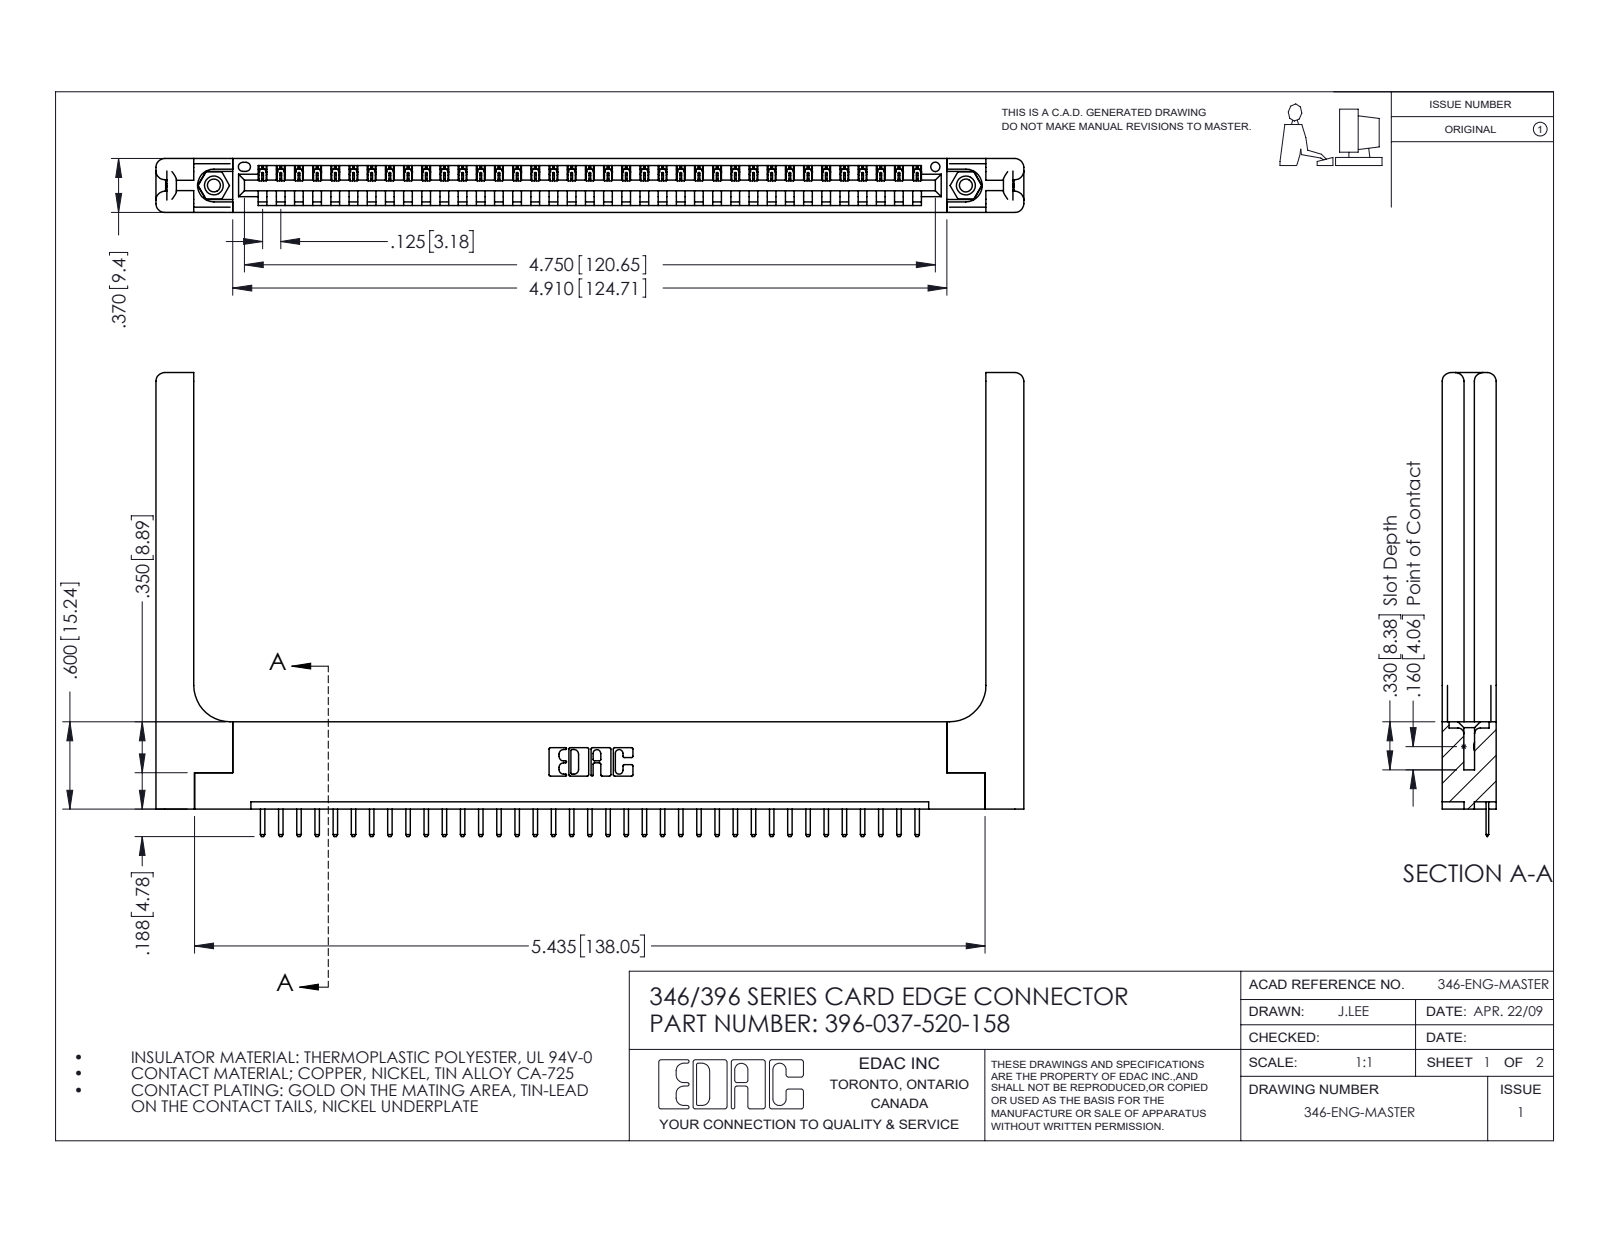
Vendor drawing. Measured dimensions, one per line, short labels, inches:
name: 345-292-001_345-293-120; 346 Part_Flush Mounting Lugs - 0.156 Dia-TH; 345-250-001_345-250-001-102; 396-037-520-158 (+1 more)
written by: SolidWorks 2016 (CONFIG_CONTROL_DESIGN)
unit: in
bodies: 42 solids, 2672 faces (1778 planar, 834 cylindrical, 60 other)
size: 5.966 × 3.188 × 0.37
volume: 1.335 in³; area: 35.21 in²
holes: 2× ⌀0.089, 2× ⌀0.125, 2× ⌀0.156, 1× ⌀0.064
bosses: 2× ⌀0.155
rounds: 76× R0.01, 74× R0.006, 22× R0.01, 16× R0.06, 6× R0.007, 6× R0.031, 3× R0.026, 2× R0.03
face distances: 0.37, 0.048, 0.322, 0.072, 0.148, 0.15, 0.25, 0.298, 0.025, 0.222
hole spacings: 0.246, 4.961, 5.17
